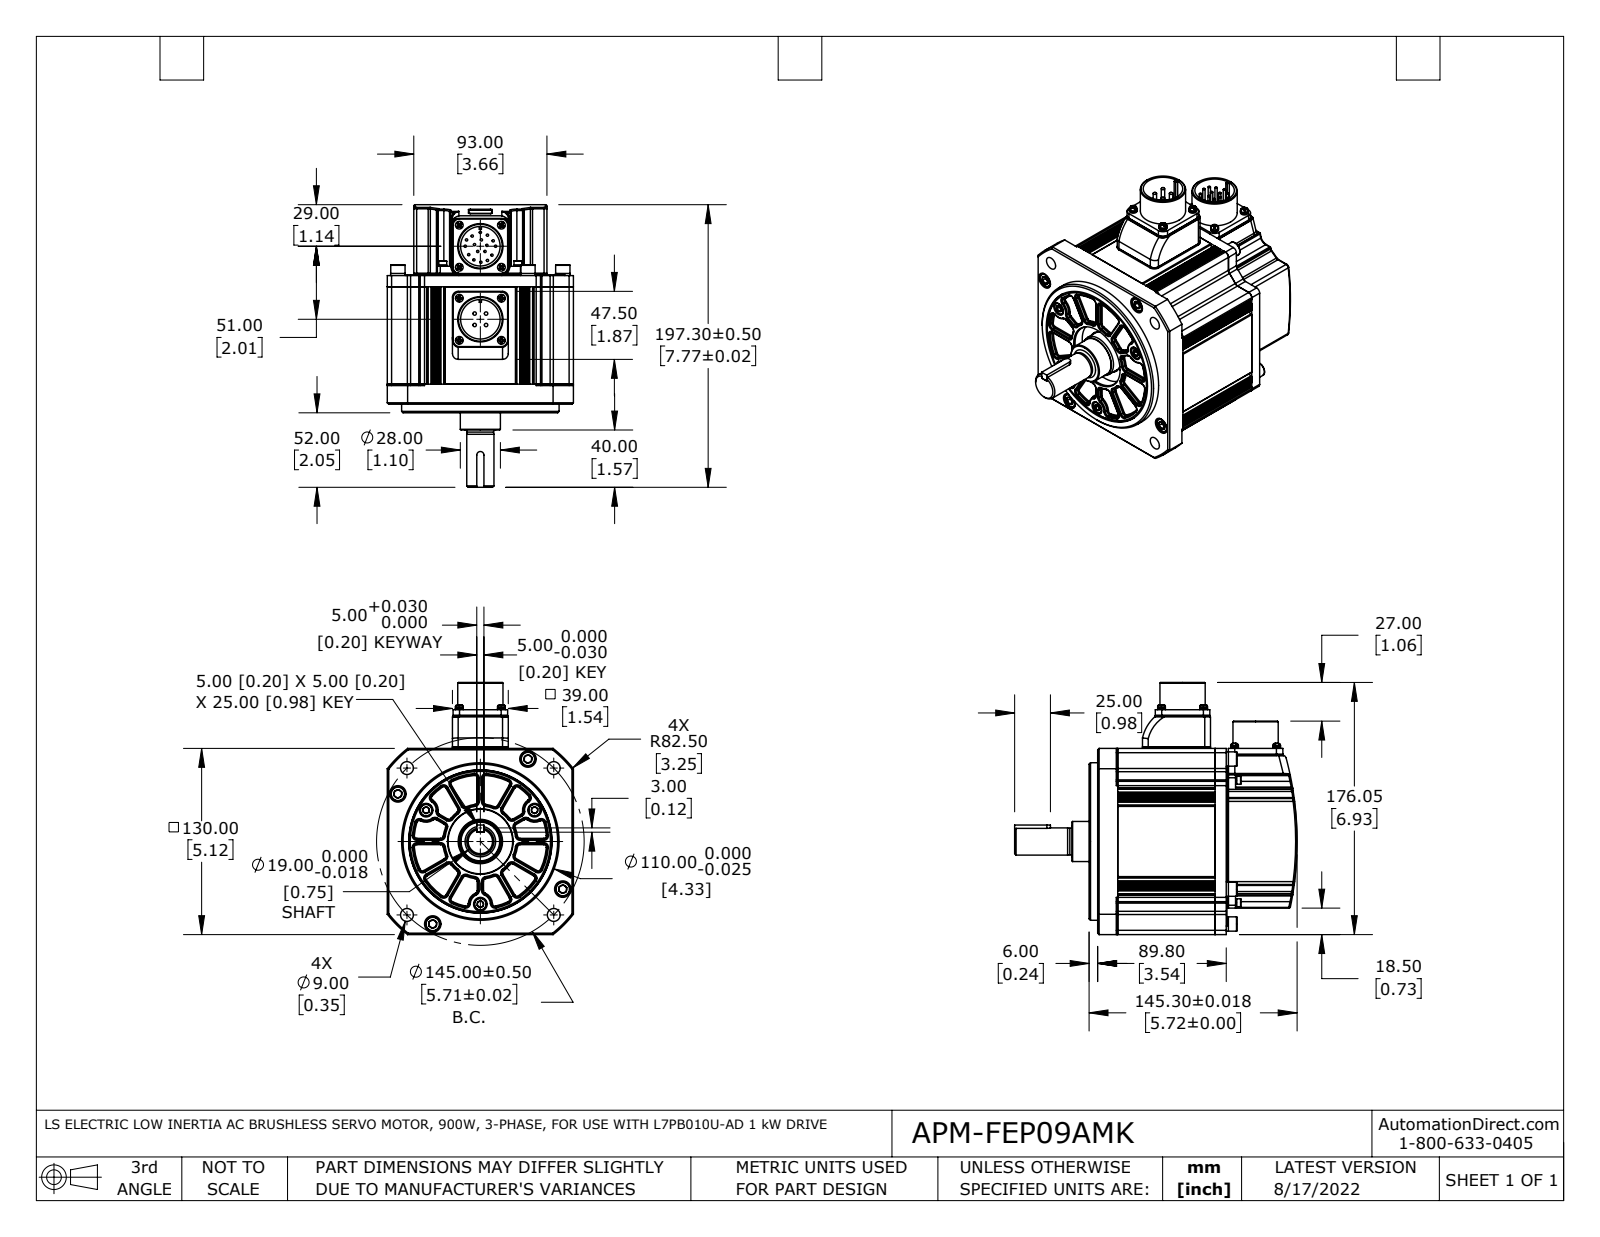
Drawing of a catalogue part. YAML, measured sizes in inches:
part_name: "FMP13GA001G01_Out Line(APM-FEP09A_K) r1 nc fxt"
step_written_by: "SolidWorks 2017 (AUTOMOTIVE_DESIGN)"
units: inches
bodies: {solids: 56, faces: 2124, planar: 706, cylindrical: 799, other: 619}
overall_size: [7.768, 6.931, 5.118]
volume: 112.3
surface_area: 430.3
round_holes:
  - {diameter: 0.098, count: 12}
  - {diameter: 0.118, count: 8}
  - {diameter: 0.12, count: 8}
  - {diameter: 0.138, count: 8}
  - {diameter: 0.197, count: 7}
  - {diameter: 0.142, count: 4}
  - {diameter: 0.146, count: 4}
  - {diameter: 0.268, count: 4}
  - {diameter: 0.276, count: 4}
  - {diameter: 0.354, count: 4}
  - {diameter: 0.453, count: 4}
  - {diameter: 0.22, count: 3}
round_bosses_or_shafts:
  - {diameter: 0.063, count: 17}
  - {diameter: 0.213, count: 8}
  - {diameter: 0.402, count: 4}
  - {diameter: 0.394, count: 4}
  - {diameter: 0.236, count: 4}
  - {diameter: 0.217, count: 4}
  - {diameter: 0.118, count: 4}
  - {diameter: 0.094, count: 4}
partial_cylinders:
  - {radius: 0.02, count: 72}
  - {radius: 0.098, count: 55}
  - {radius: 0.028, count: 24}
  - {radius: 0.079, count: 17}
  - {radius: 0.118, count: 16}
  - {radius: 0.039, count: 14}
  - {radius: 0.177, count: 12}
  - {radius: 0.157, count: 8}
face_to_face_distances: [2.677, 0.039, 3.043, 0.327, 3.004, 0.366, 3.457, 3.417, 3.091, 0.413]
hole_center_spacings: [0.819, 1.157, 2.008, 0.752, 1.041, 1.542, 1.637, 1.975]
